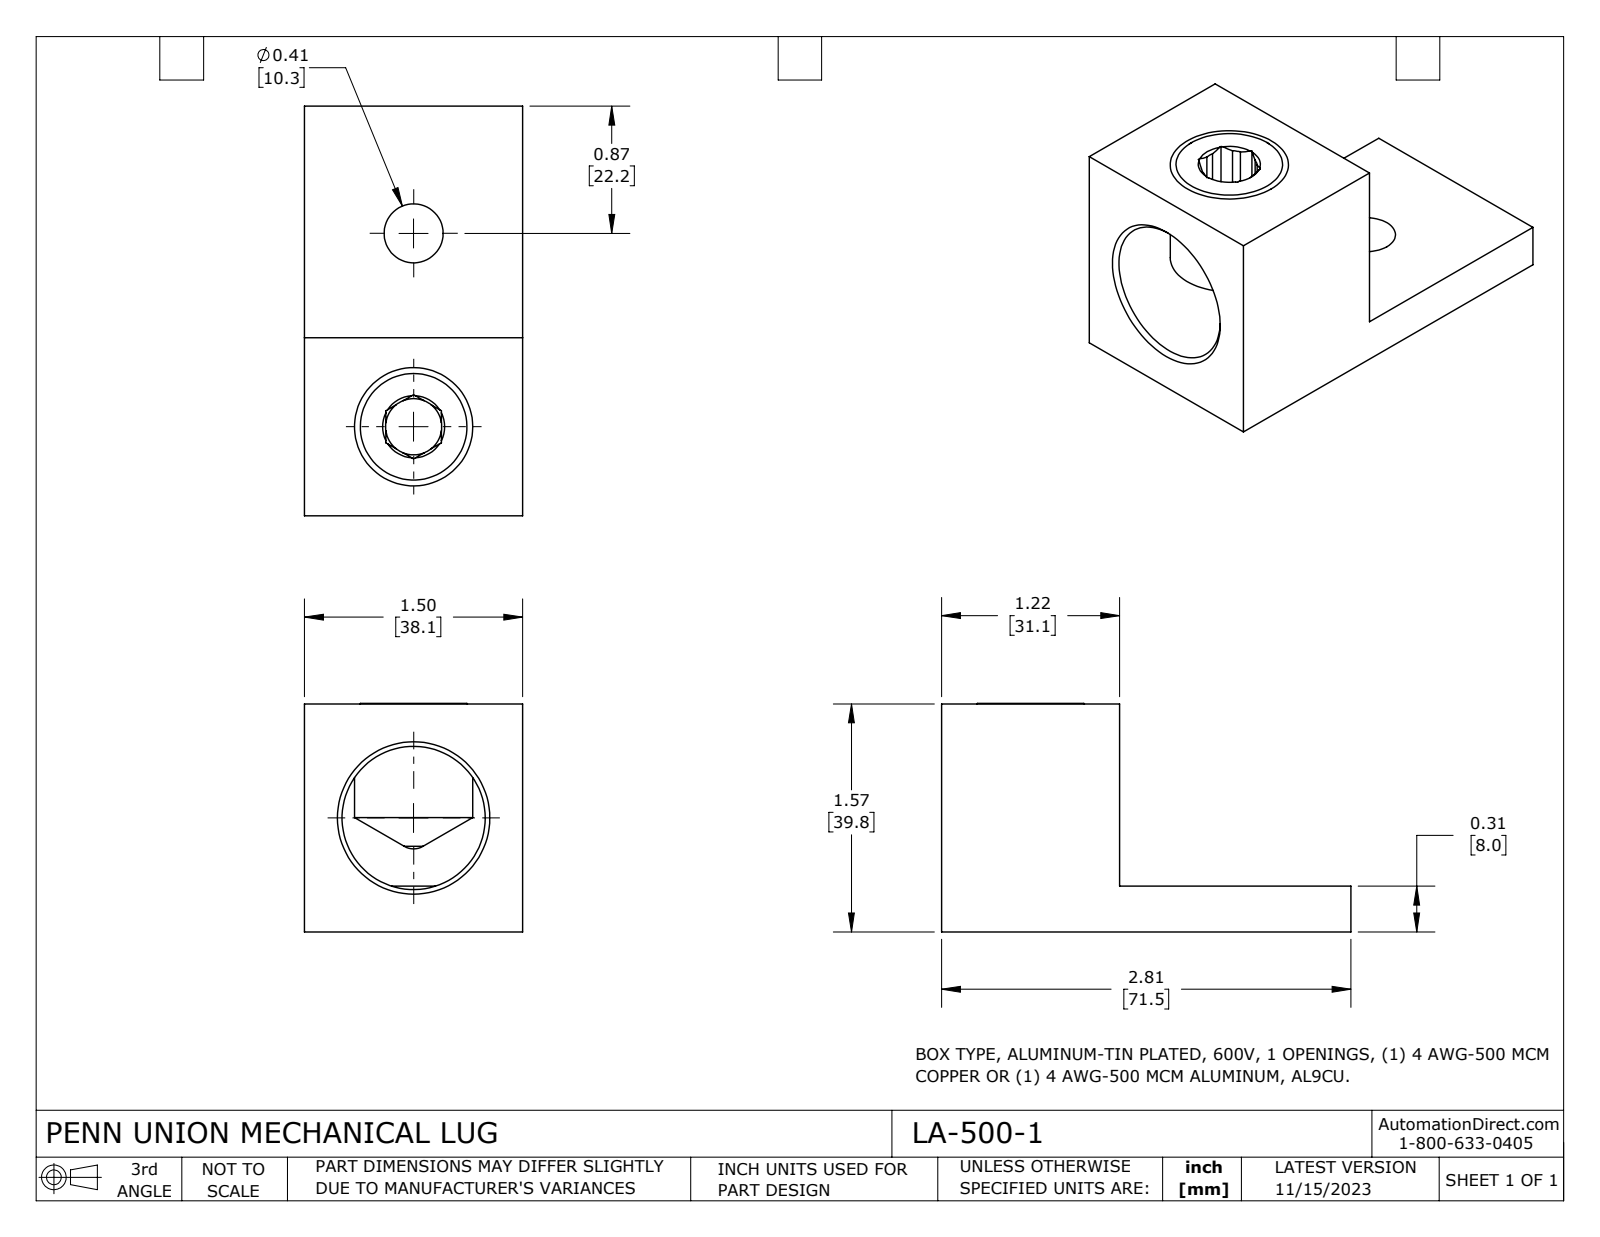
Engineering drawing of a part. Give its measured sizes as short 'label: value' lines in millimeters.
name: LA-500-1
written by: SolidWorks 2023 (CONFIG_CONTROL_DESIGN)
unit: mm
bodies: 2 solids, 56 faces (28 planar, 10 cylindrical, 18 other)
size: 71.5 × 39.9 × 38.1
volume: 47 150 mm³; area: 15 540 mm²
holes: 1× ⌀9.8, 1× ⌀10.3, 1× ⌀19.1, 1× ⌀25
bosses: 1× ⌀20.7
face distances: 38.1, 8, 39.8, 31.8, 31.1, 71.5, 40.4, 39.9, 31.9, 9.7
hole spacings: 33.8
